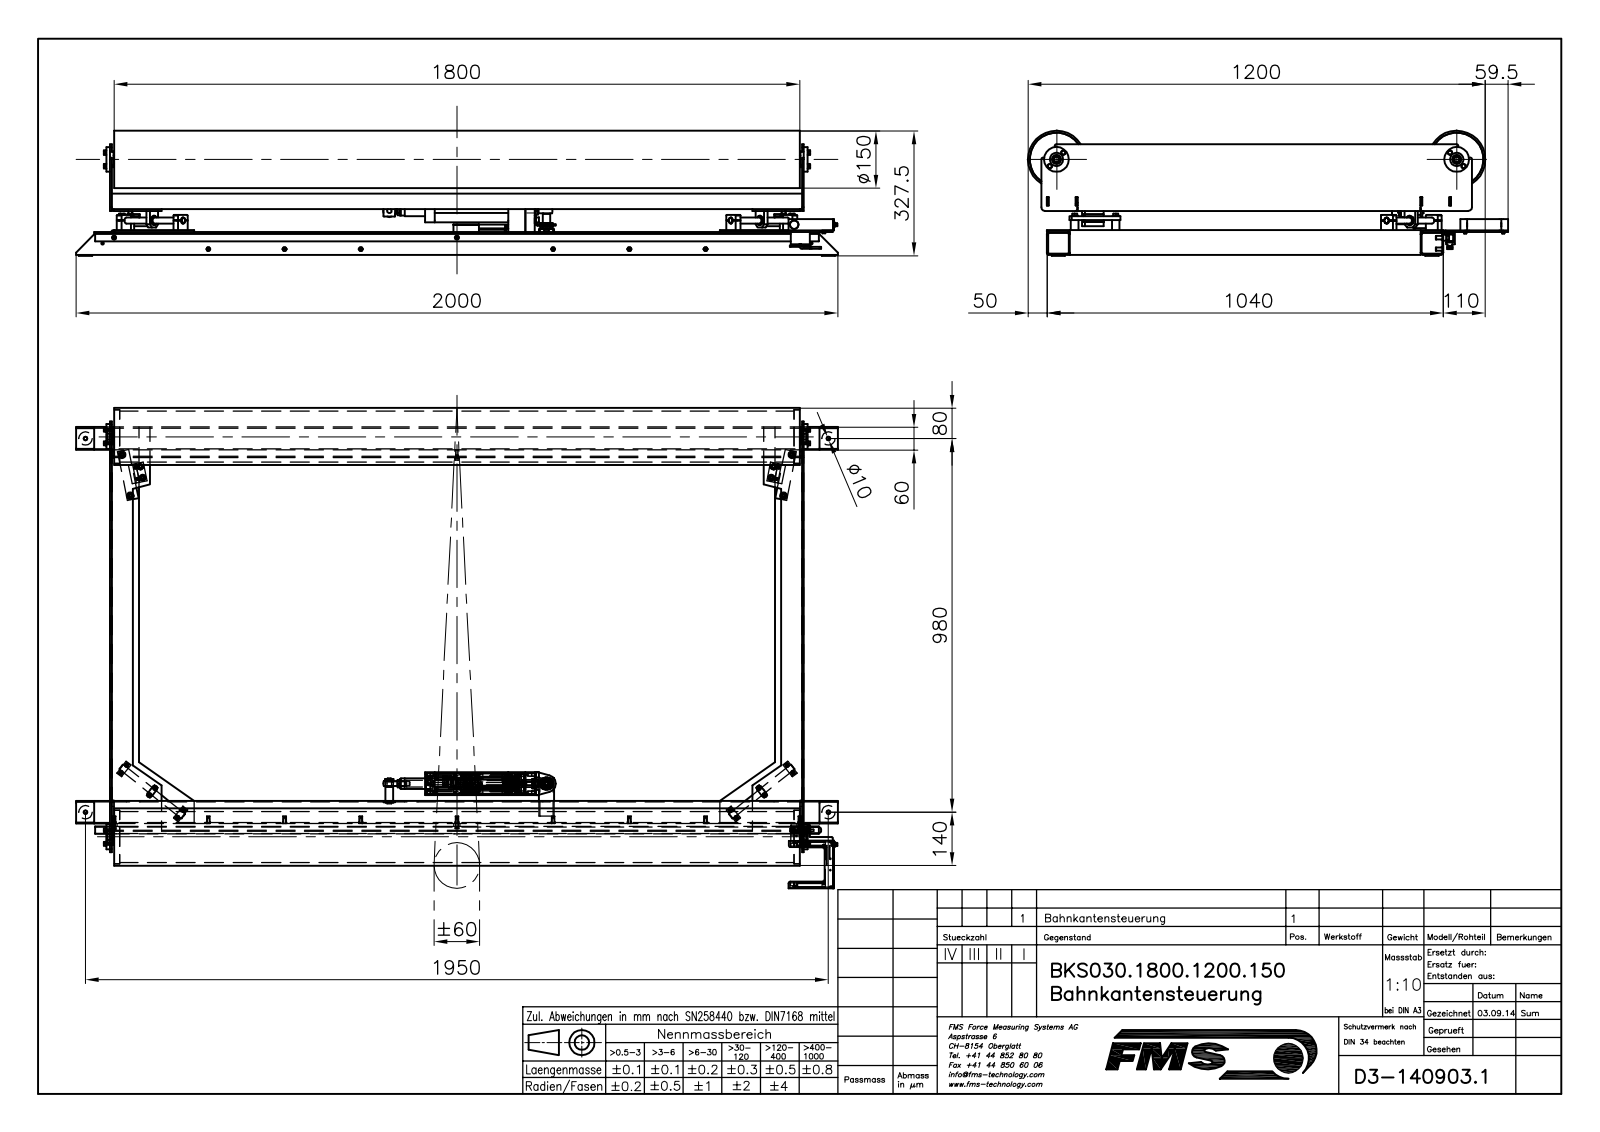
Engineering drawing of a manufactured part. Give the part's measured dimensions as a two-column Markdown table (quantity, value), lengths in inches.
| quantity | value |
| --- | --- |
| part name | K1409031; K1409032; K1409034; K1409035 (+8 more) |
| STEP written by | Mechanical Desktop 2009 (CONFIG_CONTROL_DESIGN) |
| units | inches |
| bodies | 164 solids, 2798 faces (1315 planar, 1039 cylindrical, 444 other) |
| overall size | 78.74 × 49.587 × 12.894 |
| volume | 1 458 in³ |
| surface area | 14 130 in² |
| round holes (diameter × count) | 0.203 × 35, 0.276 × 18, 0.169 × 12, 0.433 × 11, 0.331 × 10, 0.252 × 9, 0.394 × 8, 0.135 × 6, 0.63 × 6, 0.102 × 4, 0.126 × 4, 0.217 × 4 |
| round bosses / shafts (diameter × count) | 0.236 × 21, 0.354 × 17, 0.394 × 15, 0.315 × 13, 0.63 × 11, 0.472 × 11, 0.157 × 10, 0.787 × 8 |
| partial cylindrical surfaces (radius × count) | 0.039 × 22, 0.079 × 19, 0.197 × 19, 0.157 × 16, 0.118 × 8, 0.236 × 8, 0.394 × 6, 0.016 × 4 |
| main face-to-face distances | 0.118, 0.197, 2.362, 2.244, 38.583, 1.457, 2.48, 3.937, 4.724, 6.181 |
| hole center spacings | 7.874, 7.962, 1.181, 0.945, 3.74, 3.858, 35.63, 35.65 |
